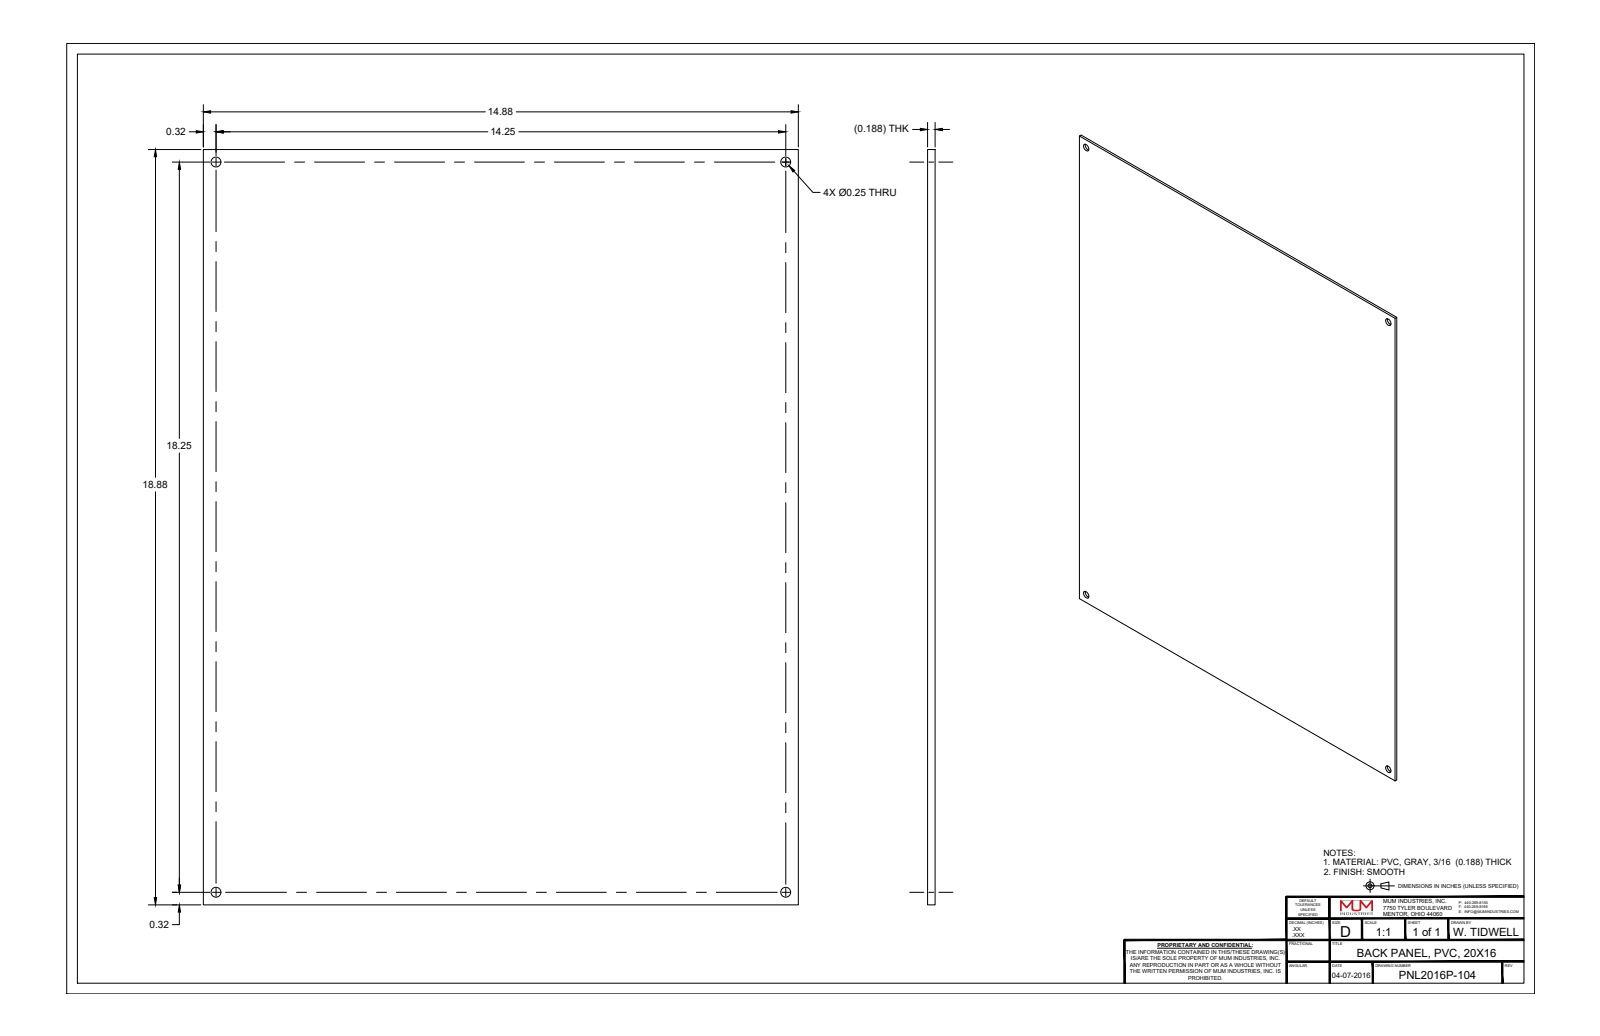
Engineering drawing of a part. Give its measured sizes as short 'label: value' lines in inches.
name: PVCBP-2016-P10
written by: SolidWorks 2018 (AUTOMOTIVE_DESIGN)
unit: in
bodies: 1 solid, 10 faces (6 planar, 4 cylindrical, 0 other)
size: 18.88 × 14.88 × 0.188
volume: 52.64 in³; area: 574.7 in²
holes: 4× ⌀0.25
face distances: 0.187, 14.88, 18.88
hole spacings: 14.25, 18.25, 23.154
